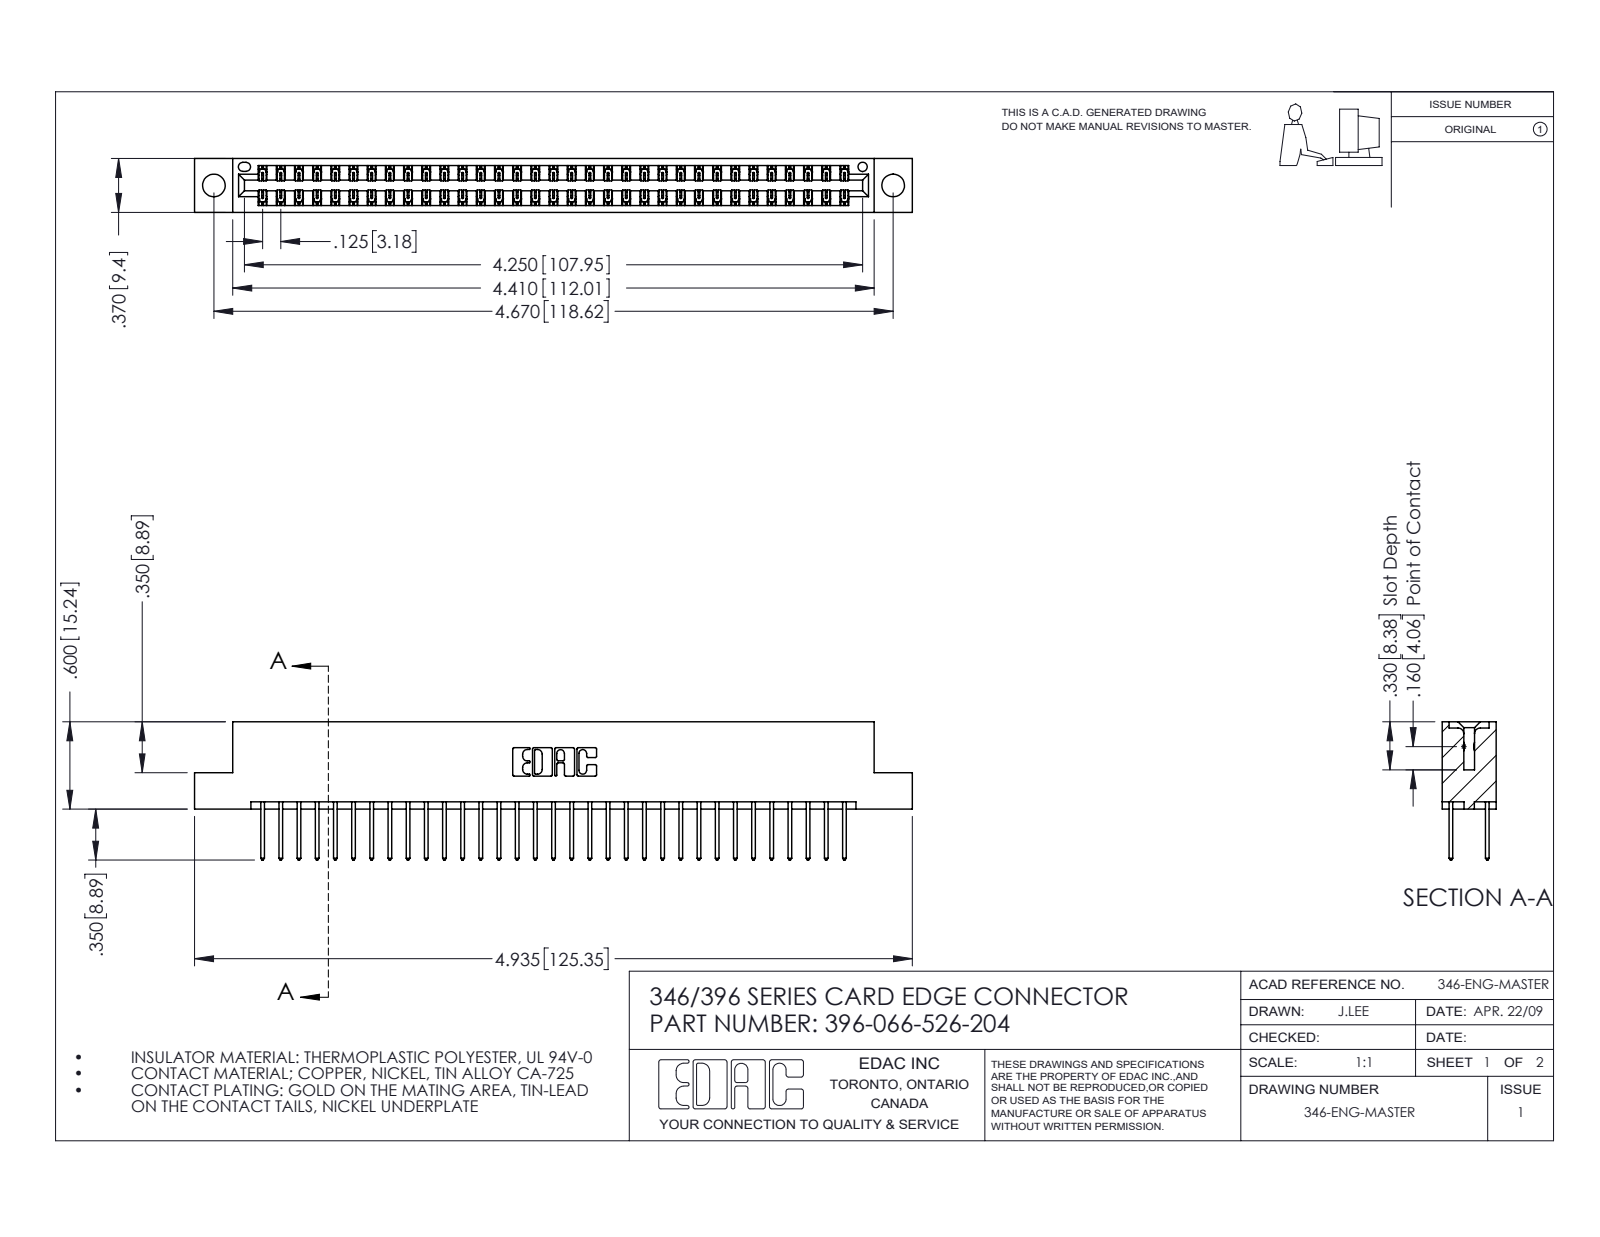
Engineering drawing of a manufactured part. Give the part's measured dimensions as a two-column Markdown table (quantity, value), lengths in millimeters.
| quantity | value |
| --- | --- |
| part name | 346 Part_Flush Mounting Lugs - 0.156 Dia-TH; 345-292-001_345-293-126; 396-066-526-204 |
| STEP written by | SolidWorks 2016 (CONFIG_CONTROL_DESIGN) |
| units | millimeters |
| bodies | 67 solids, 3554 faces (2386 planar, 1168 cylindrical, 0 other) |
| overall size | 125.3 × 24.1 × 9.4 |
| volume | 12 200 mm³ |
| surface area | 16 890 mm² |
| round holes (diameter × count) | 4 × 2, 1.6 × 1 |
| partial cylindrical surfaces (radius × count) | 0.2 × 99, 0.3 × 66, 0.3 × 22, 0.2 × 6, 0.8 × 6, 0.7 × 3, 0.4 × 2, 0.6 × 2 |
| main face-to-face distances | 1.2, 8.2, 6.4, 9.4, 1.8, 7.6, 0.6, 7, 3.8, 5.6 |
| hole center spacings | 6.2, 113.3, 118.6 |
